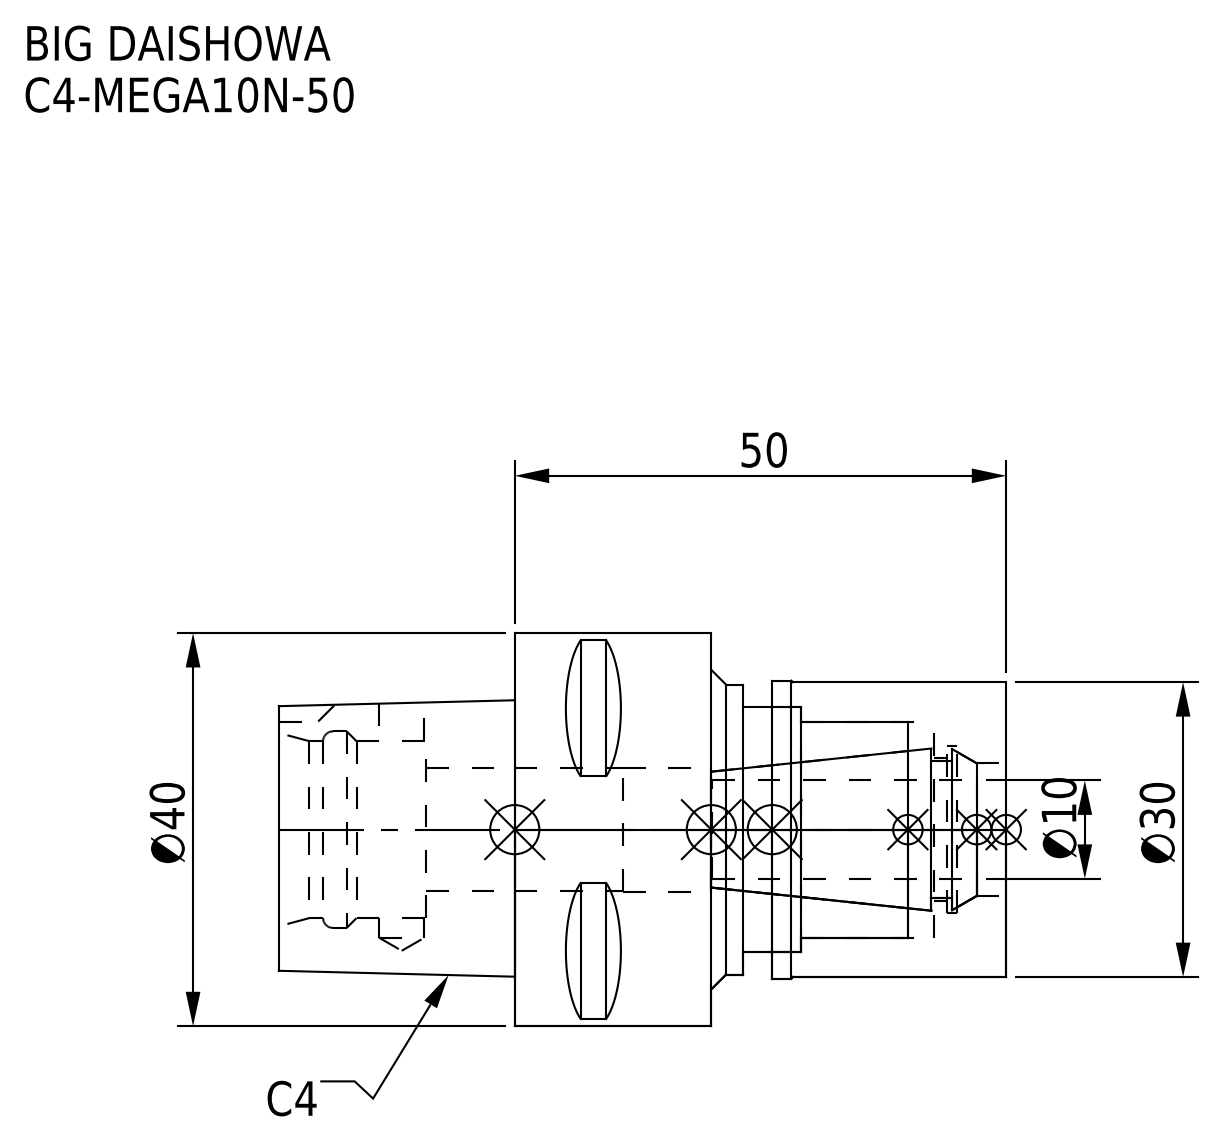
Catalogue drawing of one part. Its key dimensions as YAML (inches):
part_name: "C4-MEGA10N-50-100.stp; DXF_TEMP_ASSY_ASM_4_ASM.stp; C4-MEGA10N-50-100-FreeParts; C4-MEGA10N-50_1.stp (+3 more)"
step_written_by: "SolidWorks 2019 (CONFIG_CONTROL_DESIGN)"
units: inches
bodies: {solids: 2, faces: 92, planar: 37, cylindrical: 37, other: 18}
overall_size: [2.913, 1.575, 1.575]
volume: 2.826
surface_area: 25.17
round_holes:
  - {diameter: 0.181, count: 1}
  - {diameter: 0.492, count: 1}
  - {diameter: 0.496, count: 1}
  - {diameter: 0.531, count: 1}
  - {diameter: 0.571, count: 1}
  - {diameter: 0.669, count: 1}
  - {diameter: 0.709, count: 1}
  - {diameter: 0.787, count: 1}
  - {diameter: 0.866, count: 1}
  - {diameter: 0.984, count: 1}
round_bosses_or_shafts:
  - {diameter: 1.575, count: 1}
  - {diameter: 1.193, count: 1}
  - {diameter: 1.181, count: 1}
  - {diameter: 1.161, count: 1}
partial_cylinders:
  - {radius: 0.118, count: 1}
face_to_face_distances: [0.787, 1.969, 1.181, 0.945, 1.732, 0.65, 0.937, 0.244, 1.031, 0.823]
